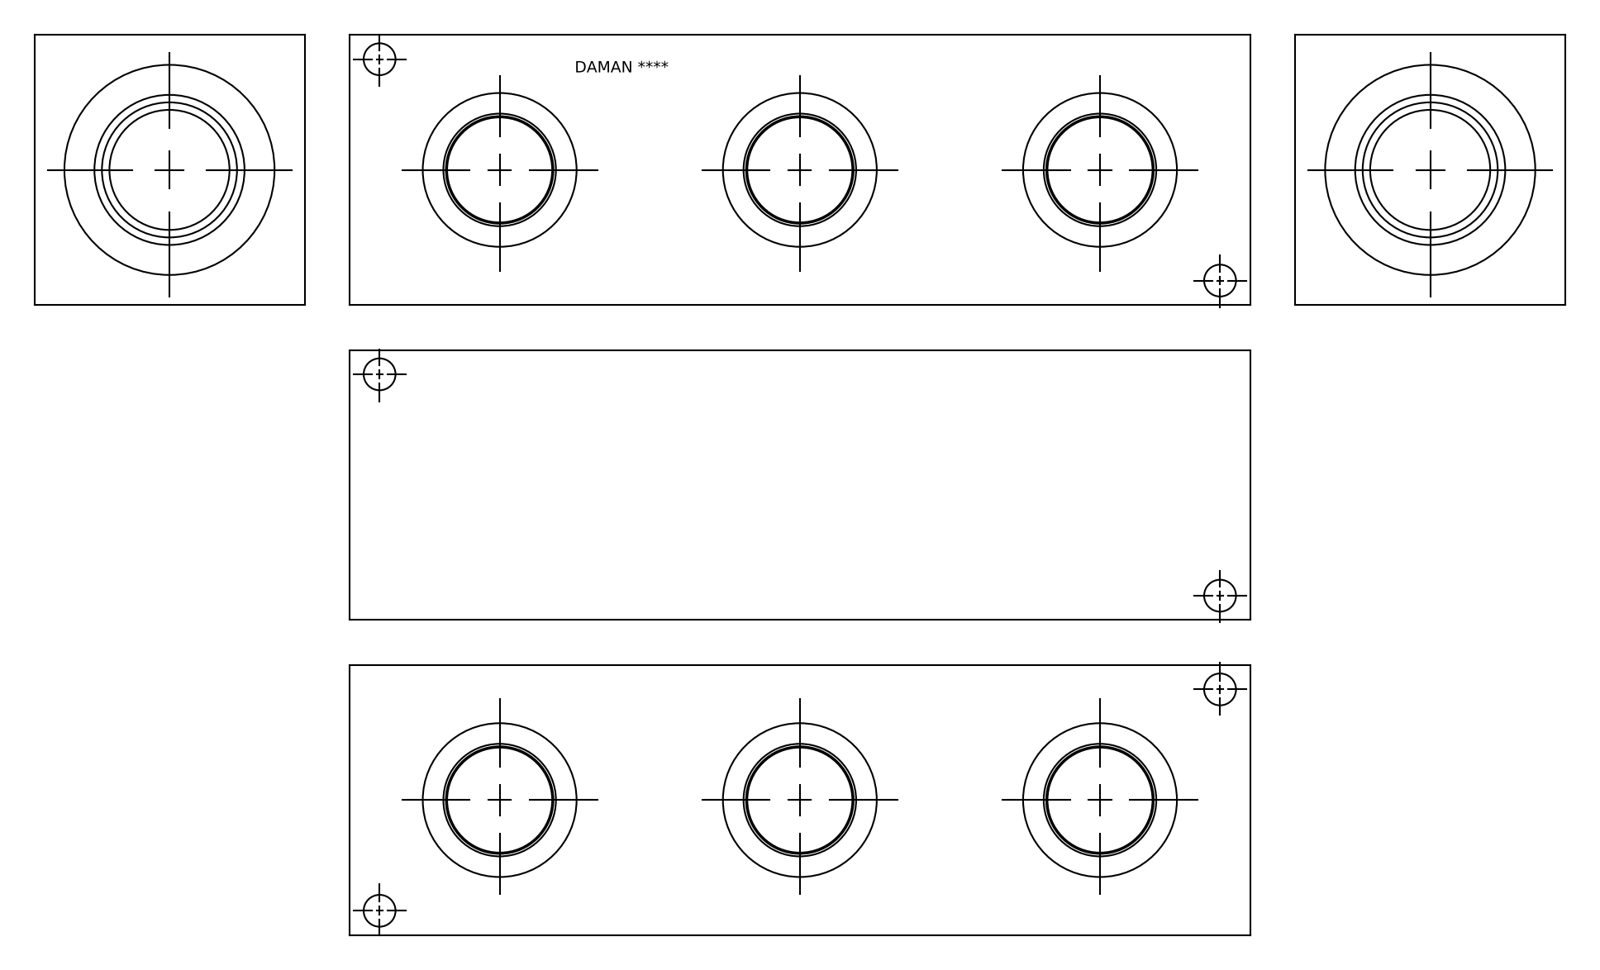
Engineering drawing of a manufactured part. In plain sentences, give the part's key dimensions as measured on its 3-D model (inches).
The part is named "Part_+H1800324S_3D". Its 3-D file was written by "Autodesk Inventor 2020 (AUTOMOTIVE_DESIGN)". It is 1 solid with 424 faces: 246 planar, 48 cylindrical and 130 other. Overall it measures 15 by 4.5 by 4.5 inches. Its volume is 260 cubic inches and its surface area 408.6 square inches. Round holes: 4 of diameter 0.531, 3 of diameter 1.688, 3 of diameter 1.794, 3 of diameter 1.875, 3 of diameter 1.892, 3 of diameter 2.564, 1 of diameter 2, 1 of diameter 2.419, 1 of diameter 2.5, 1 of diameter 2.518, 1 of diameter 3.47. The main face-to-face distances are 4.5, 0.031, 4.469, 15, 14.969, 4.438, 14.938, 0.781, 0.75, 3.719. The hole center spacings are 2.72, 5, 7.239, 12.141, 14.478, 10.
